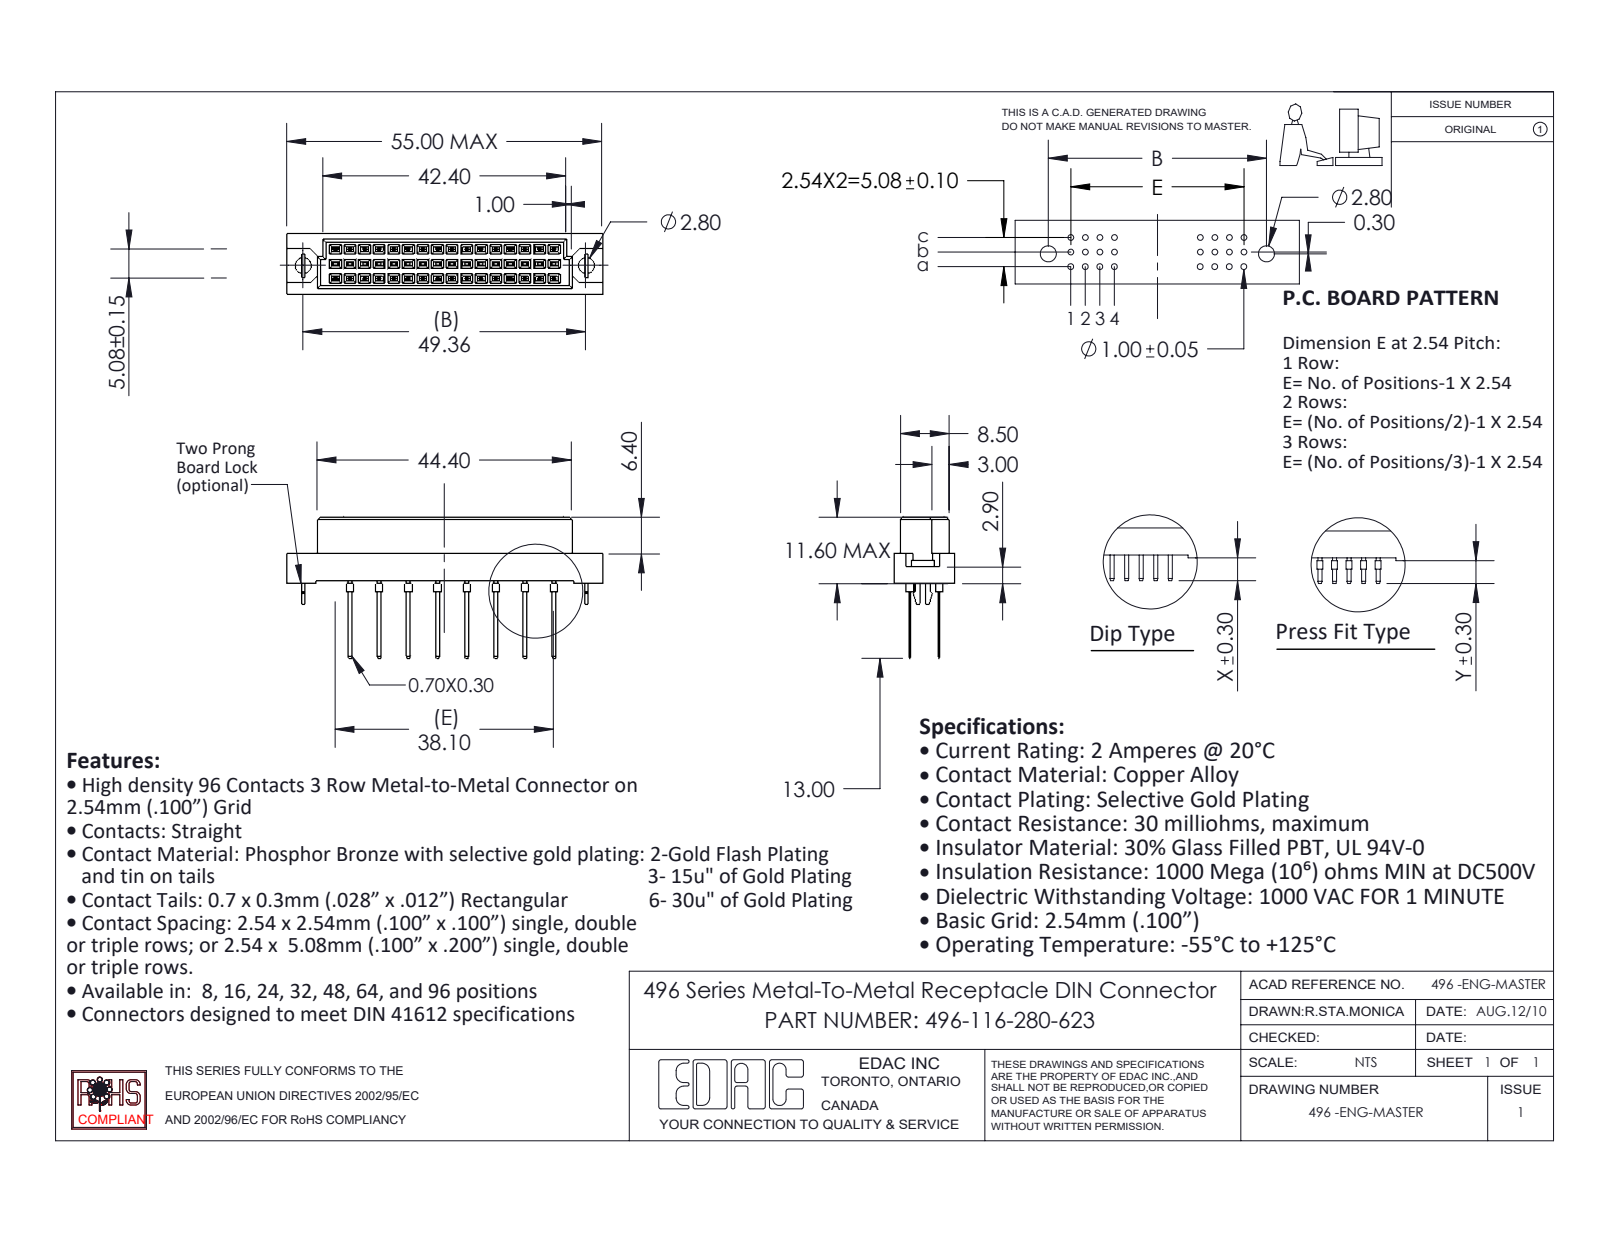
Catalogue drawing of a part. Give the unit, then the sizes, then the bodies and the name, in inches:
Units: inches
Overall size (bounding box): 2.165 × 0.969 × 0.417
Round holes (diameter × count): ⌀0.11 ×2
Round bosses / shafts (diameter × count): ⌀0.039 ×16
Partial cylindrical surfaces — rounded edges, fillets, slot ends (radius × count): R0.021 ×1
Main face-to-face distances: 0.1, 0.2, 0.041, 0.376, 0.032, 0.022, 0.022, 0.061, 0.073, 0.103
Hole centre spacings: 1.943
Volume: 0.286 in³ · Surface area: 7.649 in²
Bodies: 19 solids, 990 faces (952 planar, 38 cylindrical, 0 other)
Part name (STEP PRODUCT): 496-116-280-623; 496 Part_48; 496-290_80; 496 Bore-lock
STEP written by: SolidWorks 2020 (CONFIG_CONTROL_DESIGN)
